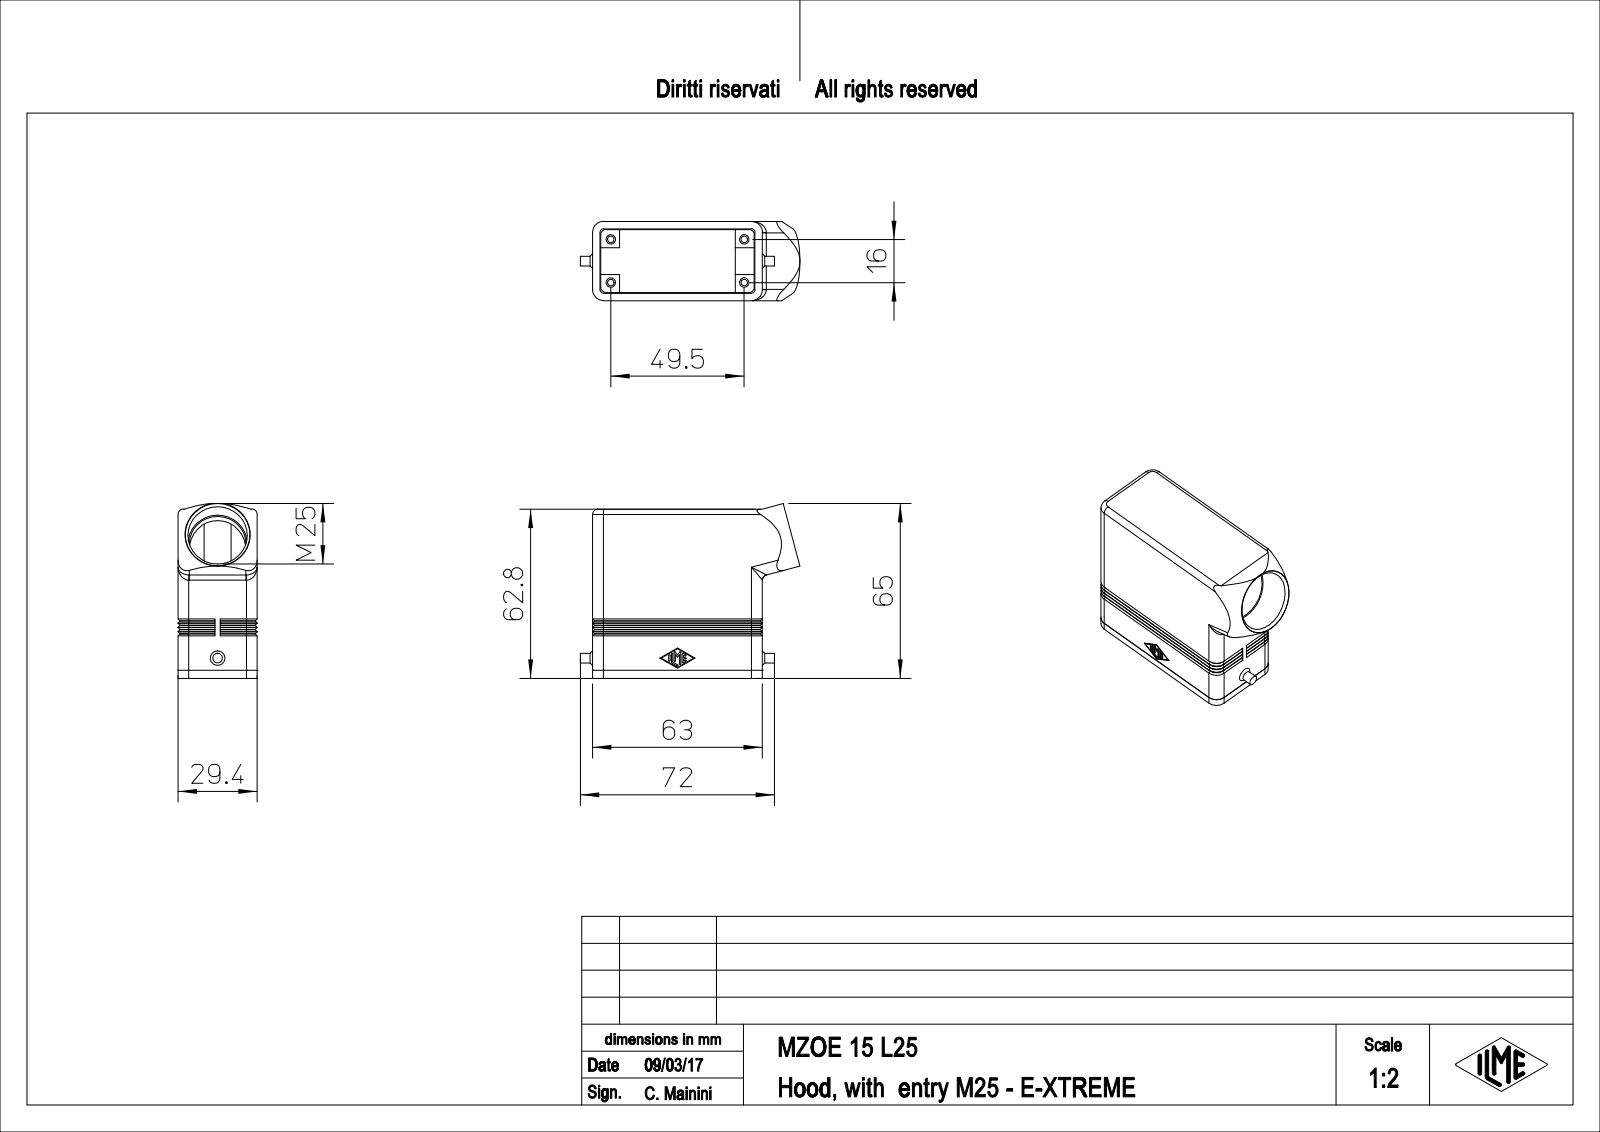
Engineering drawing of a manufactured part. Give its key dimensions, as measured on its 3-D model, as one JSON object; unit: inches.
{"part_name": "MZOE_15_L25", "step_written_by": "PTC Creo Elements/Direct Modeling 19.0E 27-Jun-2016 (C) Parametric Technology GmbH (AUTOMOTIVE_DESIGN)", "units": "inches", "bodies": {"solids": 1, "faces": 323, "planar": 177, "cylindrical": 92, "other": 54}, "overall_size": [3.209, 2.555, 1.158], "volume_in3": 2.723, "surface_area_in2": 40.93, "round_holes": [[0.097, 4], [0.138, 4], [0.827, 1], [0.866, 1]], "round_bosses_or_shafts": [[0.142, 1]], "partial_cylinders_radius": [[0.01, 14], [0.079, 8], [0.157, 8], [0.049, 4], [0.13, 4], [0.165, 2]], "face_to_face_distances": [0.118, 1.039, 1.157, 0.921, 0.394, 2.087, 2.362, 0.276, 1.969, 0.382], "hole_center_spacings": [0.63, 1.949, 2.048]}
